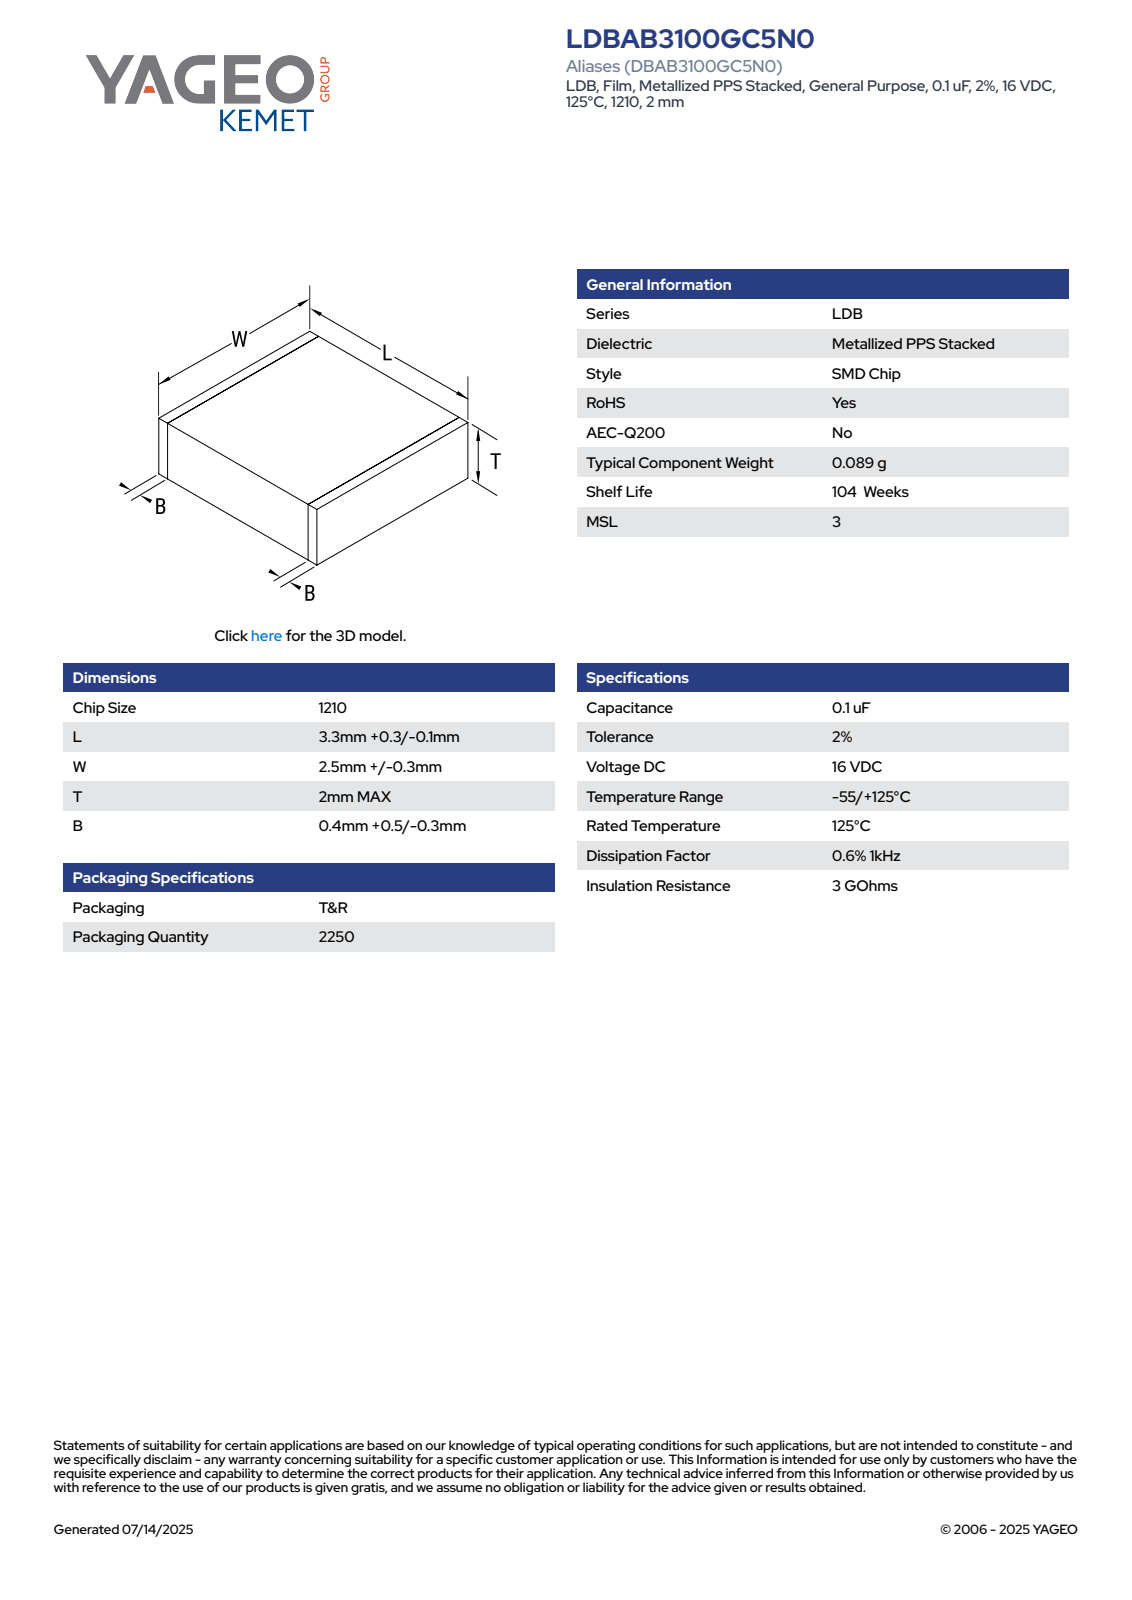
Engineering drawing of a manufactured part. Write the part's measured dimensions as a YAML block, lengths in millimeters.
part_name: "CFS_LDELDB_1210_L3.6W2.8T2B0.9"
step_written_by: "SolidWorks 2020 (AUTOMOTIVE_DESIGN)"
units: millimeters
bodies: {solids: 4, faces: 73, planar: 73, cylindrical: 0, other: 0}
overall_size: [3.6, 2.8, 2]
volume: 20
surface_area: 46
face_to_face_distances: [1.98, 3.6, 1.99, 2.78, 2.79, 2, 2.8, 0.5, 3.1, 2.6]
